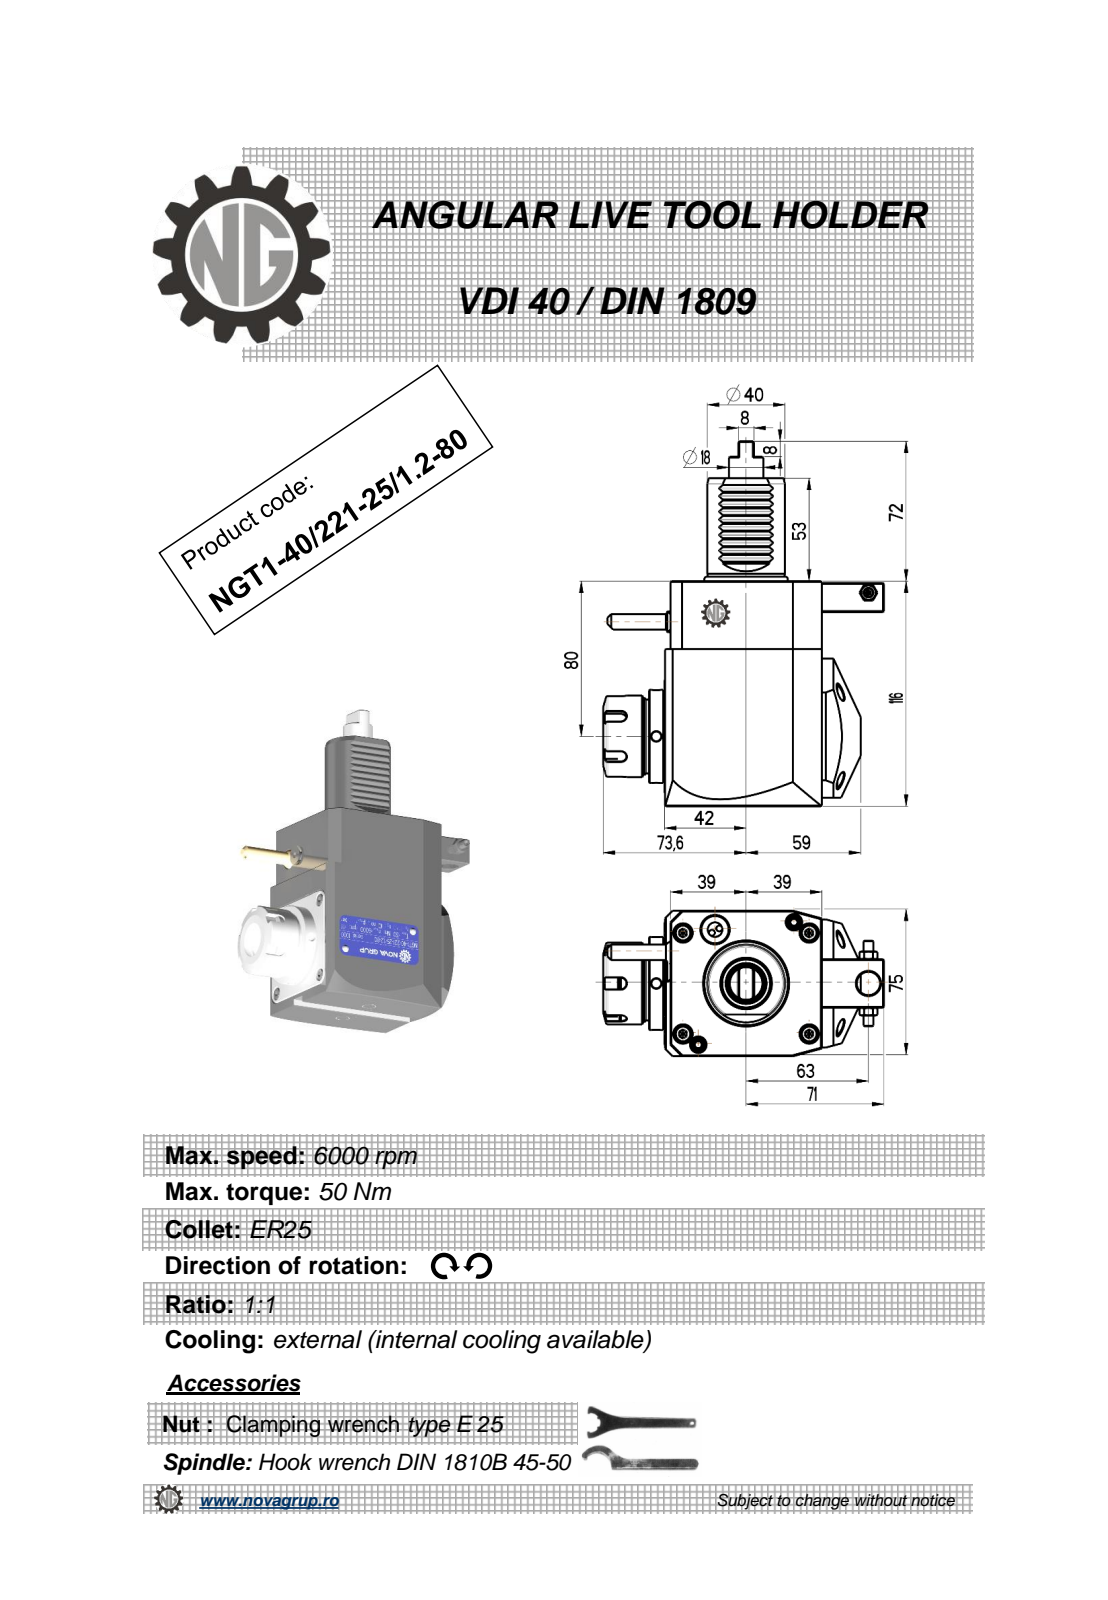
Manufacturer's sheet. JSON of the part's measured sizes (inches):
{"part_name": "NGT1_40_221_25_1_2_80", "step_written_by": "PRO/ENGINEER BY PARAMETRIC TECHNOLOGY CORPORATION, 2010280 (CONFIG_CONTROL_DESIGN)", "units": "inches", "bodies": {"solids": 1, "faces": 463, "planar": 202, "cylindrical": 100, "other": 161}, "overall_size": [7.402, 5.693, 3.016], "volume_in3": 52.26, "surface_area_in2": 107, "round_holes": [[0.197, 3], [0.118, 1], [0.165, 1], [0.374, 1], [0.472, 1], [0.799, 1], [1.016, 1]], "round_bosses_or_shafts": [[1.575, 2], [1.89, 1], [1.654, 1], [1.496, 1], [0.701, 1], [0.441, 1], [0.353, 1], [0.315, 1]], "partial_cylinders_radius": [[0.01, 12], [0.012, 10], [0.009, 6], [0.118, 5], [0.031, 2], [0.02, 1], [0.547, 1], [0.65, 1]], "face_to_face_distances": [2.953, 4.567, 3.189, 0.118, 3.071, 0.11, 3.181, 0.984, 0.295, 0.02], "hole_center_spacings": [0.059, 0.824, 2.407, 2.423, 2.854, 2.855, 4.301, 5.195]}
